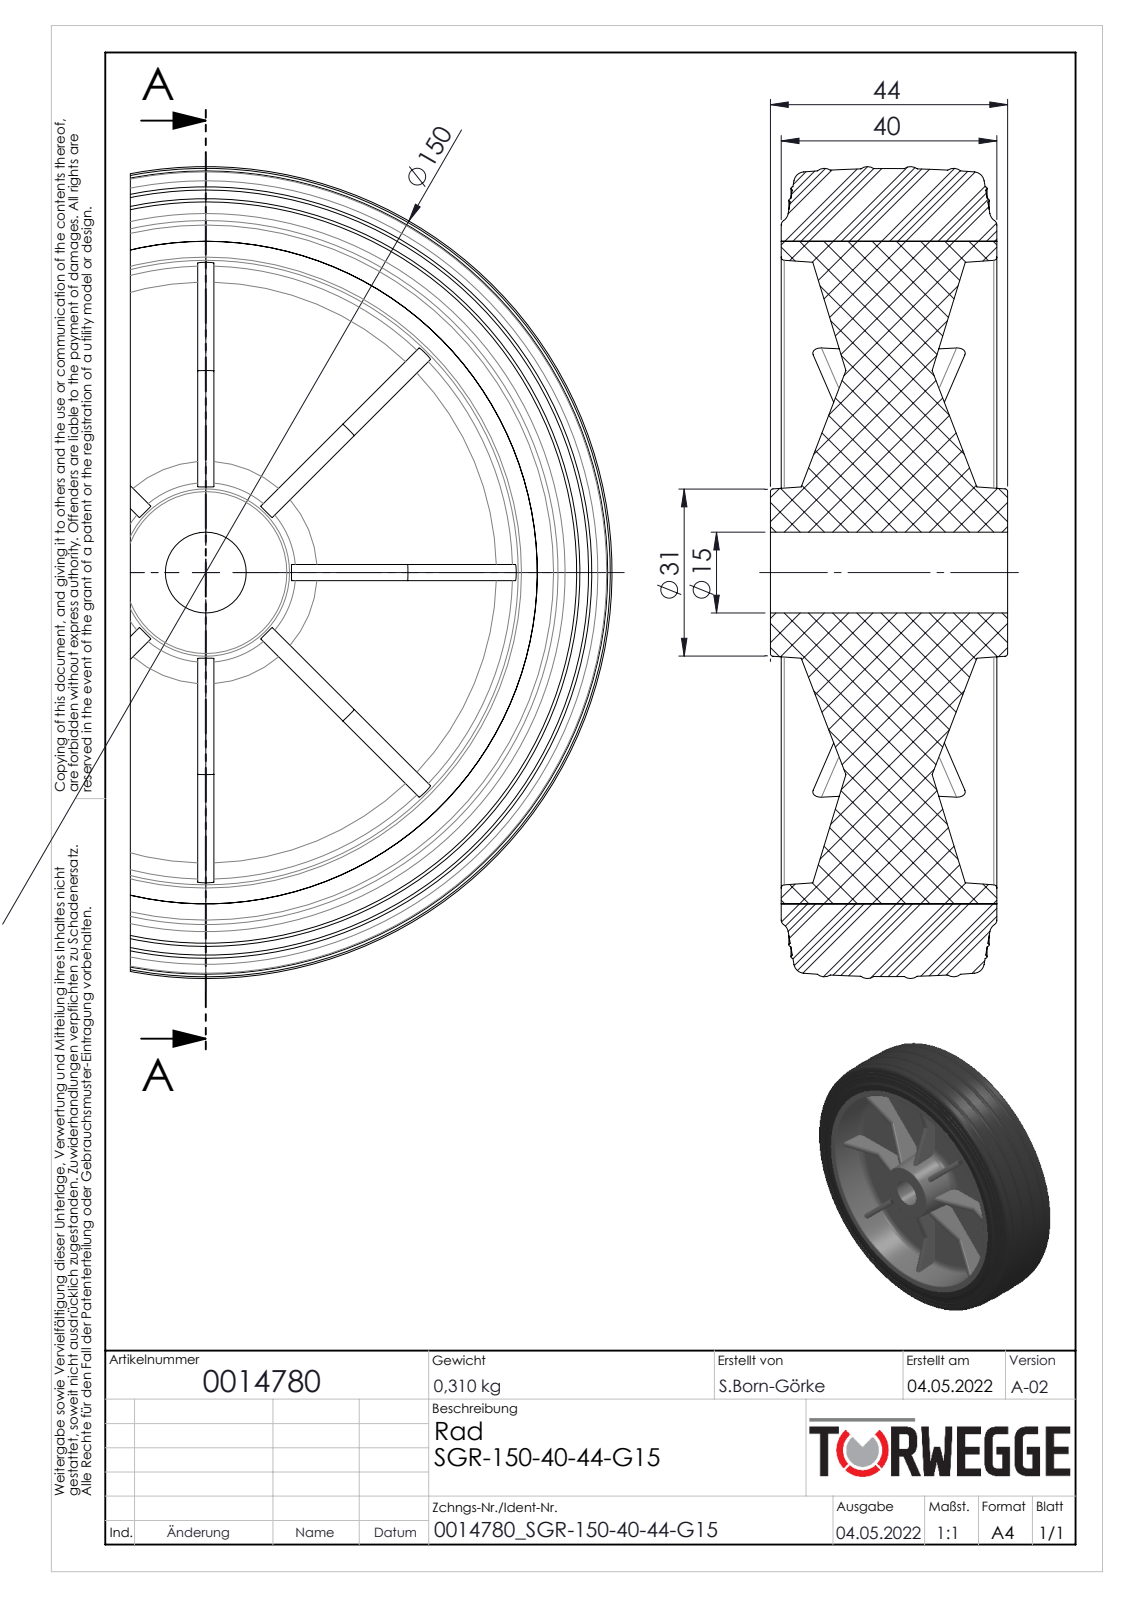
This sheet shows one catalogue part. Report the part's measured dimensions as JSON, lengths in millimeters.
{"part_name": "0014780", "step_written_by": "SolidWorks 2020 (AUTOMOTIVE_DESIGN)", "units": "millimeters", "bodies": {"solids": 2, "faces": 214, "planar": 54, "cylindrical": 46, "other": 114}, "overall_size": [150.72, 150.72, 44], "volume_mm3": 351939, "surface_area_mm2": 110788, "round_holes": [[15, 1], [123, 1]], "partial_cylinders_radius": [[1.5, 32]], "face_to_face_distances": [3, 18.5, 21.5, 40, 2, 20.5, 23.5, 42, 44]}
